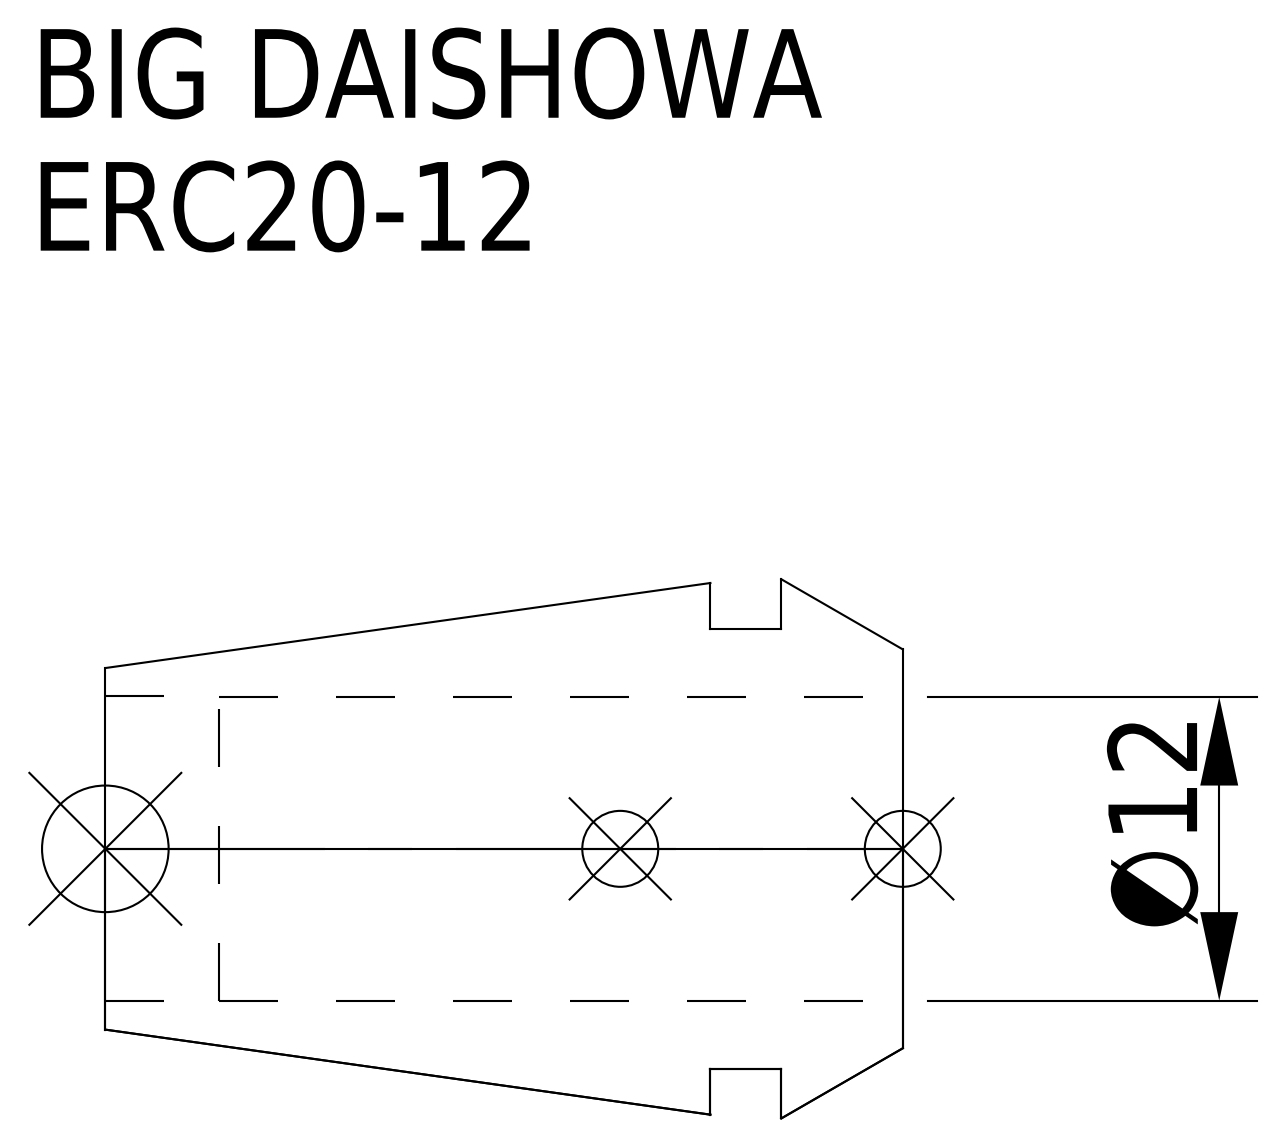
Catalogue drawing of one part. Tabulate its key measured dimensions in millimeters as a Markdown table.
| quantity | value |
| --- | --- |
| part name | ERC20-12 |
| STEP written by | CREO PARAMETRIC BY PTC INC, 2016380 (AUTOMOTIVE_DESIGN) |
| units | millimeters |
| bodies | 1 solid, 15 faces (5 planar, 6 cylindrical, 4 other) |
| overall size | 31.5 × 21.3 × 21.3 |
| volume | 4 316 mm³ |
| surface area | 3 358 mm² |
| round holes (diameter × count) | 12 × 1, 12.05 × 1 |
| round bosses / shafts (diameter × count) | 17.4 × 1 |
| main face-to-face distances | 2.8, 4.8, 7.6, 31.5, 26.7, 23.9, 27, 22.2, 19.4, 4.5 |
